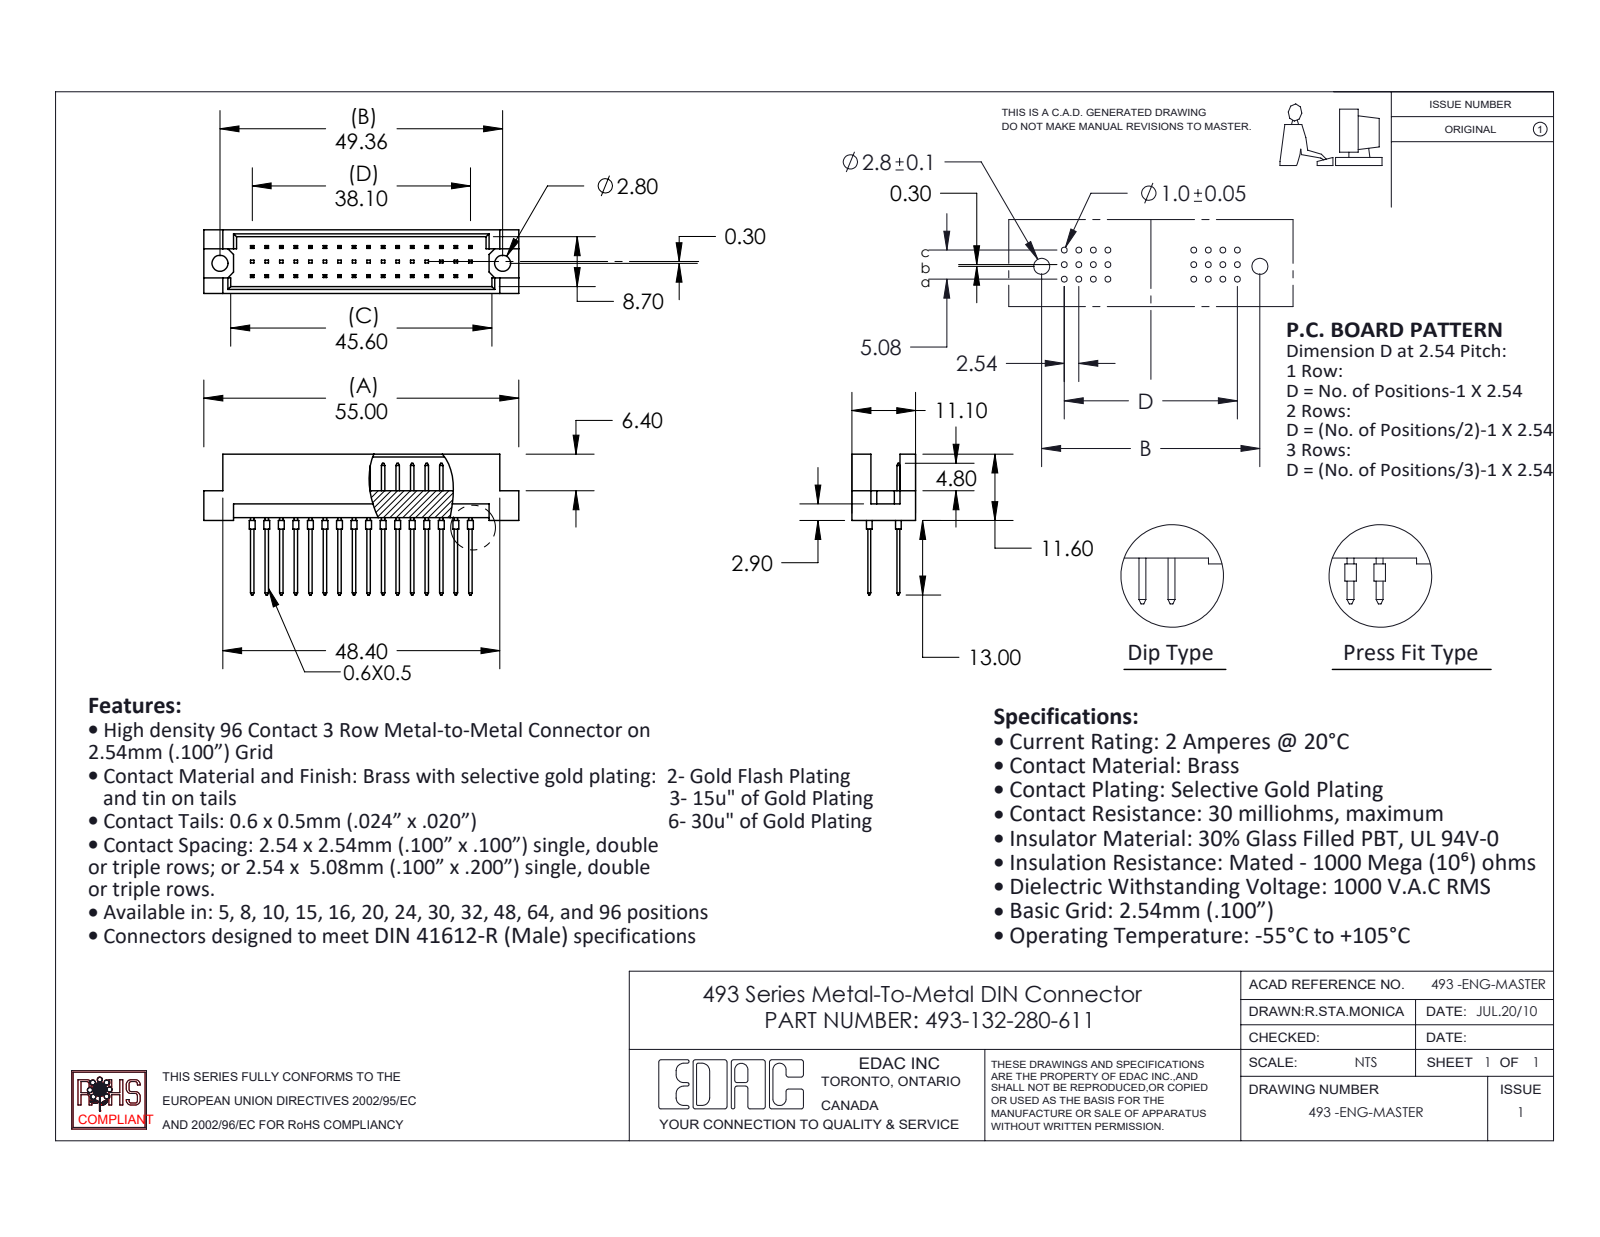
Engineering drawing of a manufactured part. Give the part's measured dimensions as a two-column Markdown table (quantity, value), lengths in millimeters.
| quantity | value |
| --- | --- |
| part name | 493-132-280-611; 493 Part_48; 493-290_80 |
| STEP written by | SolidWorks 2020 (CONFIG_CONTROL_DESIGN) |
| units | millimeters |
| bodies | 33 solids, 948 faces (880 planar, 68 cylindrical, 0 other) |
| overall size | 55 × 24.6 × 11.1 |
| volume | 3 513 mm³ |
| surface area | 5 439 mm² |
| round holes (diameter × count) | 2.8 × 2 |
| round bosses / shafts (diameter × count) | 1 × 32 |
| main face-to-face distances | 5.08, 1.2, 9.9, 0.5, 2.54, 11.1, 2.76, 8.34, 1.56, 7.14 |
| hole center spacings | 49.36 |
